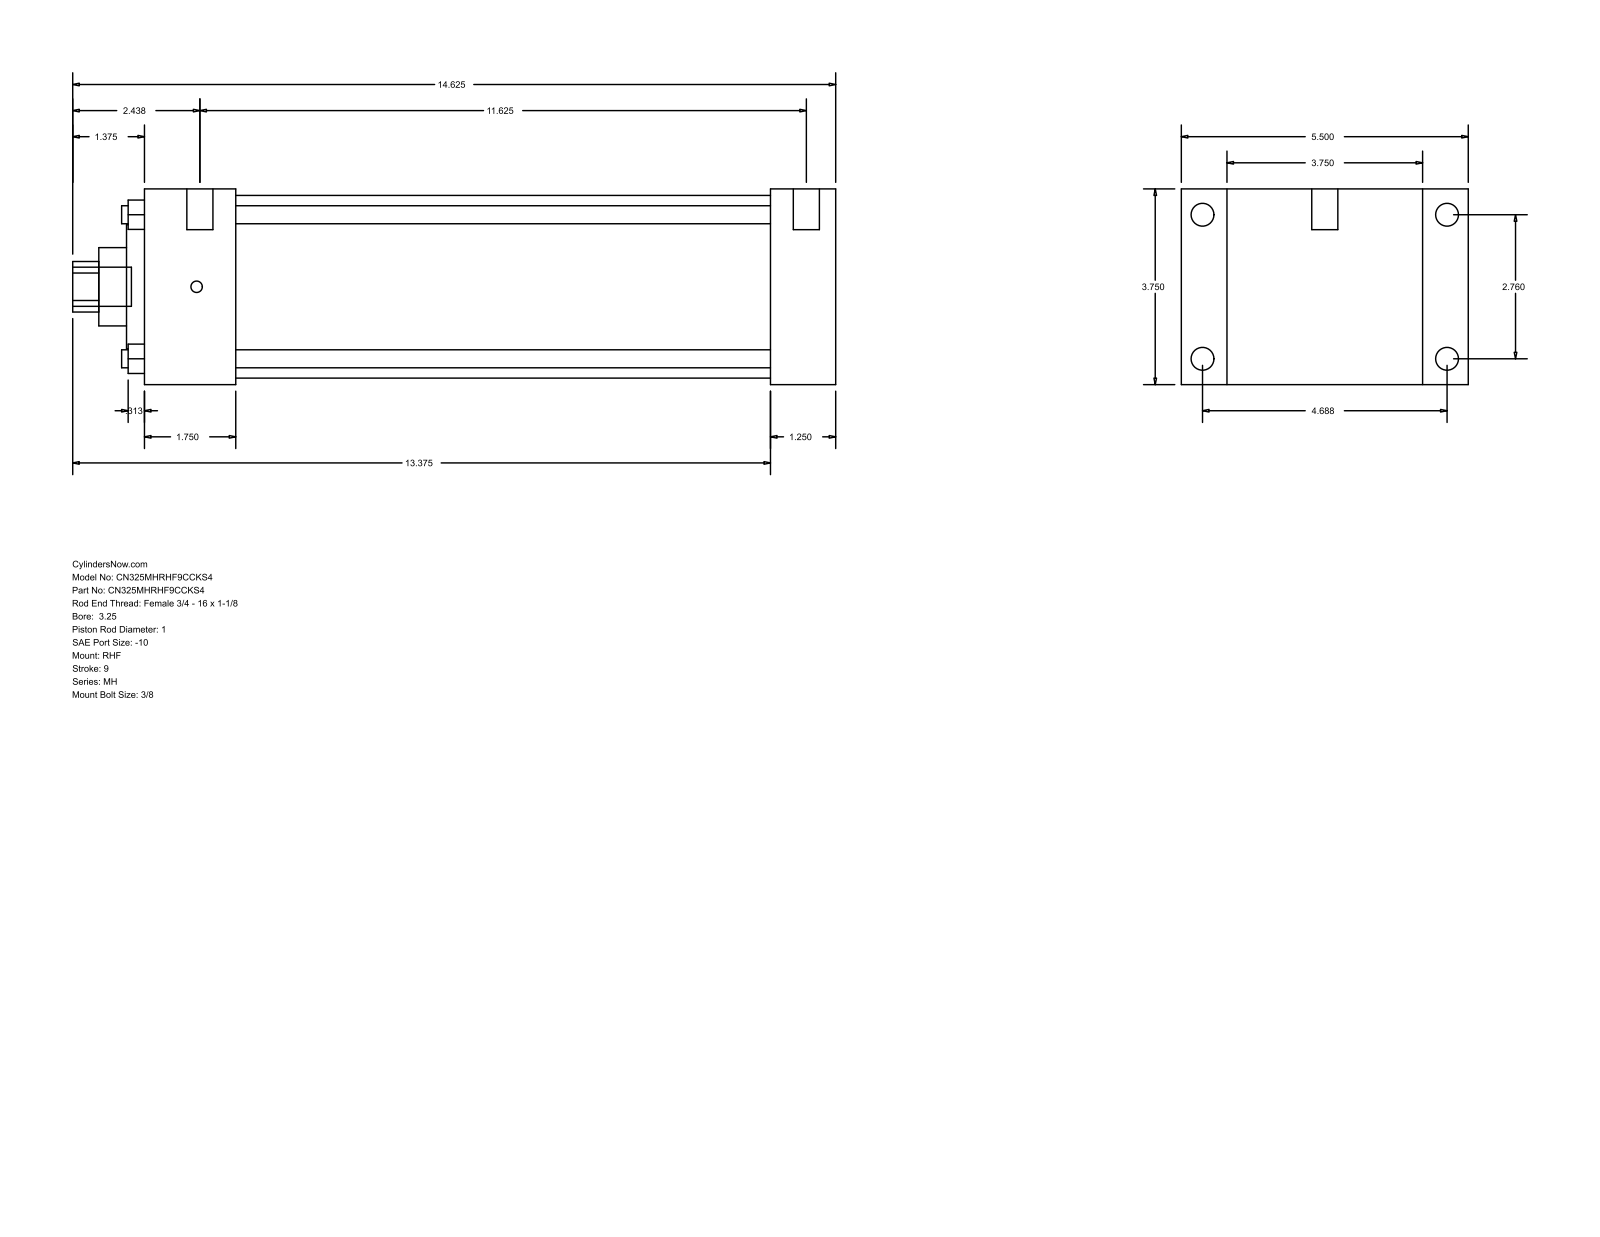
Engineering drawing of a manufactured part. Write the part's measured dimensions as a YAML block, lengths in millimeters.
part_name: "MH_RHF__0325_1"
step_written_by: "GSSL Pune (CONFIG_CONTROL_DESIGN)"
units: millimeters
bodies: {solids: 0, faces: 90, planar: 61, cylindrical: 29, other: 0}
overall_size: [371.48, 139.7, 95.25]
round_holes:
  - {diameter: 8.76, count: 4}
  - {diameter: 25.4, count: 1}
  - {diameter: 38.1, count: 1}
  - {diameter: 60.33, count: 1}
  - {diameter: 88.9, count: 1}
round_bosses_or_shafts:
  - {diameter: 11.13, count: 4}
  - {diameter: 5.56, count: 4}
  - {diameter: 12.7, count: 2}
  - {diameter: 19.05, count: 1}
partial_cylinders:
  - {radius: 12.29, count: 1}
face_to_face_distances: [95.24, 31.75, 22.23, 117.47, 304.81, 336.56, 139.7, 44.46, 260.35, 292.1]
hole_center_spacings: [49.57, 70.1, 99.14]
